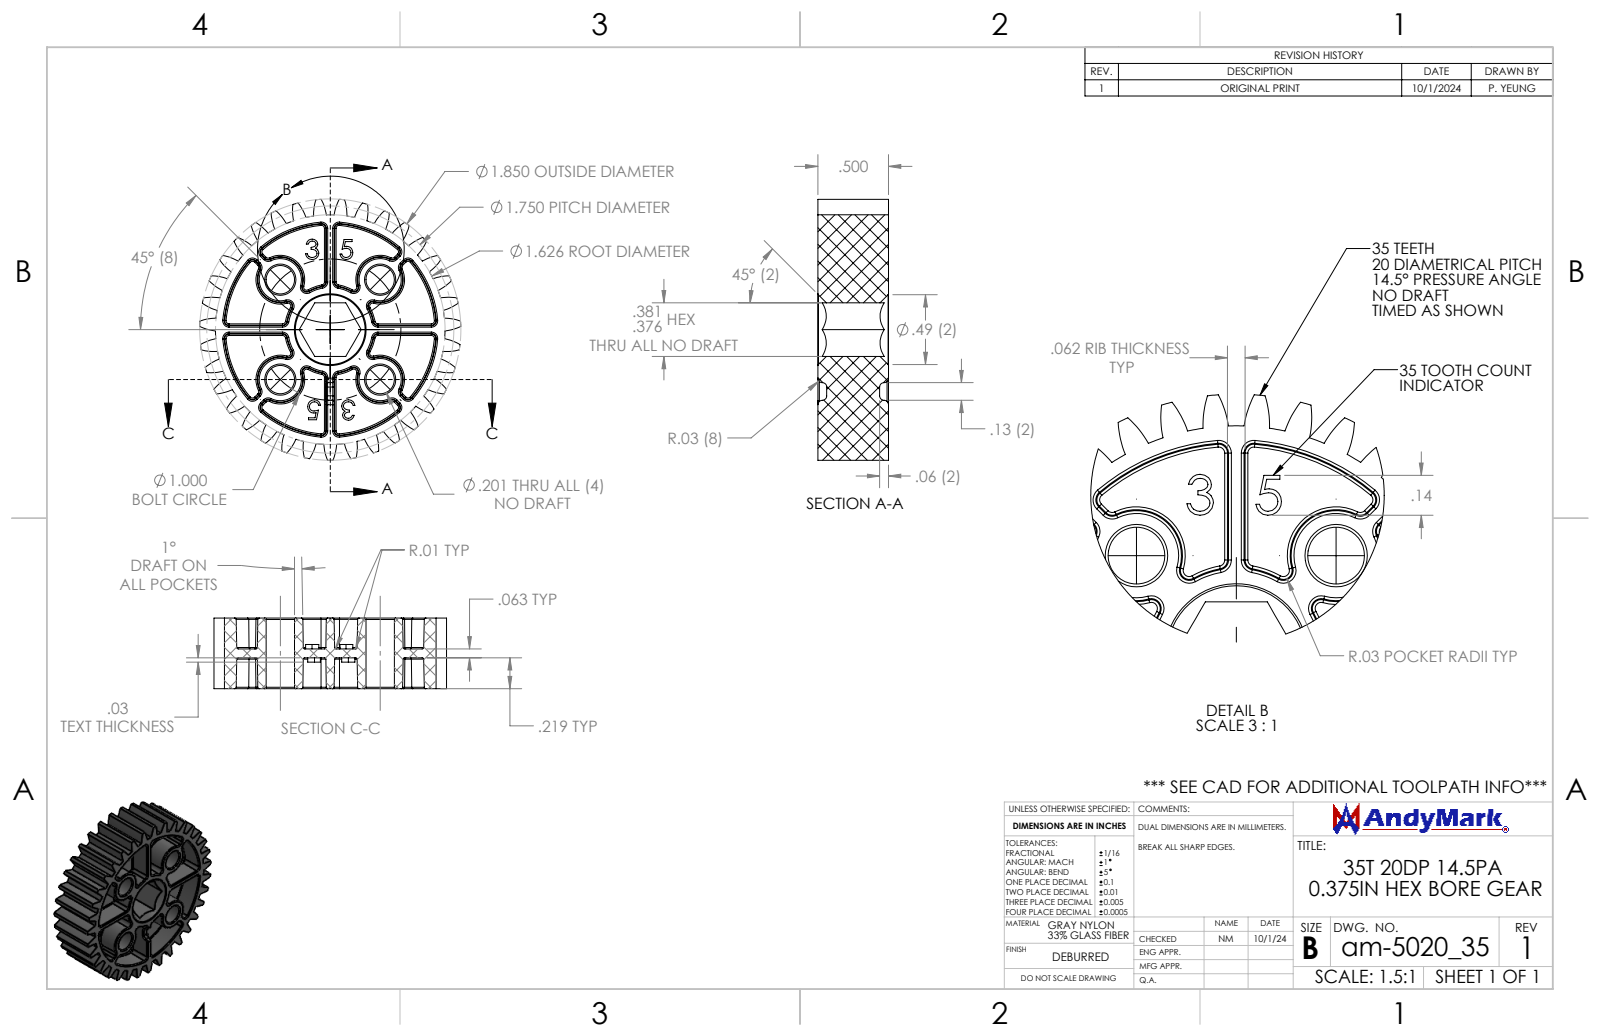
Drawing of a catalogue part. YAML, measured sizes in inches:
part_name: "am-5020_35 35T 20DP 14.5PA 0.50 IN FW 0.375 Hex Gear"
step_written_by: "SolidWorks 2024 (AUTOMOTIVE_DESIGN)"
units: inches
bodies: {solids: 1, faces: 930, planar: 102, cylindrical: 232, other: 596}
overall_size: [1.849, 1.848, 0.5]
volume: 0.611
surface_area: 17.24
round_holes:
  - {diameter: 0.201, count: 4}
partial_cylinders:
  - {radius: 0.35, count: 70}
  - {radius: 0.01, count: 38}
  - {radius: 0.031, count: 8}
  - {radius: 0.813, count: 1}
  - {radius: 0.925, count: 1}
face_to_face_distances: [0.219, 0.281, 0.5, 0.062, 0.064, 0.38, 0.187, 0.313, 0.031, 0.094]
hole_center_spacings: [0.707, 1]
